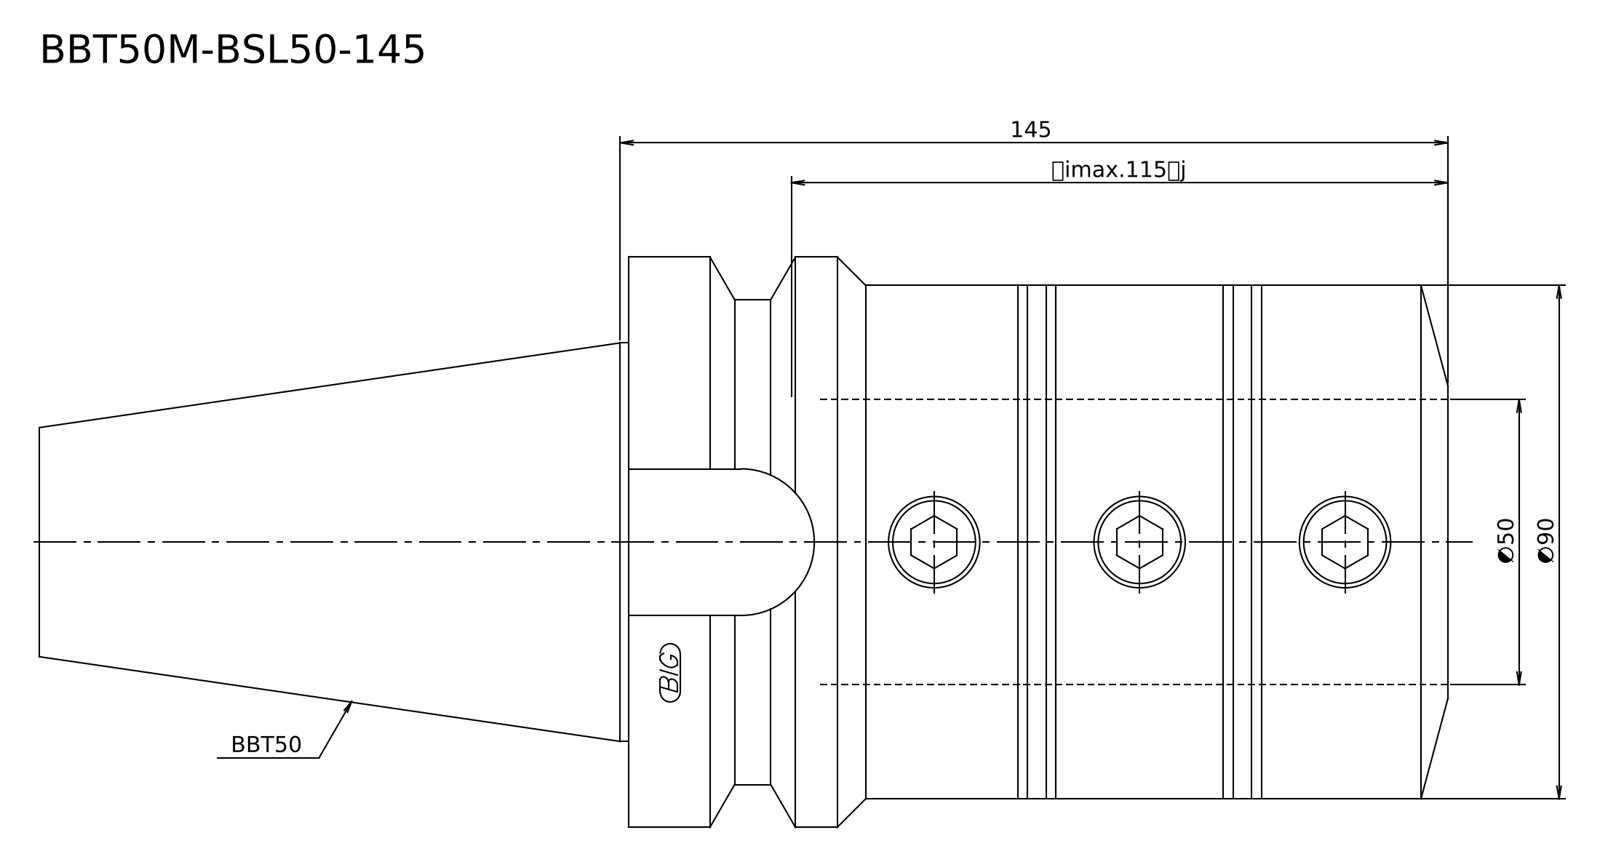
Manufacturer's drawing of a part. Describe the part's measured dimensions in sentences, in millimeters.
Its 3-D file was written by "Kubotek KeyCreator 2011 V10.0.2 (22737) (automotive_design)". It is 1 solid with 13 faces: 3 planar, 5 cylindrical and 5 other. Overall it measures 246.8 by 100 by 100 millimeters. Its volume is 1 191 000 cubic millimeters and its surface area 73 002 square millimeters. Round bosses or shafts: 1 of diameter 100, 1 of diameter 90, 1 of diameter 85, 1 of diameter 69.85. The main face-to-face distances are 143.5, 246.8, 103.3.
